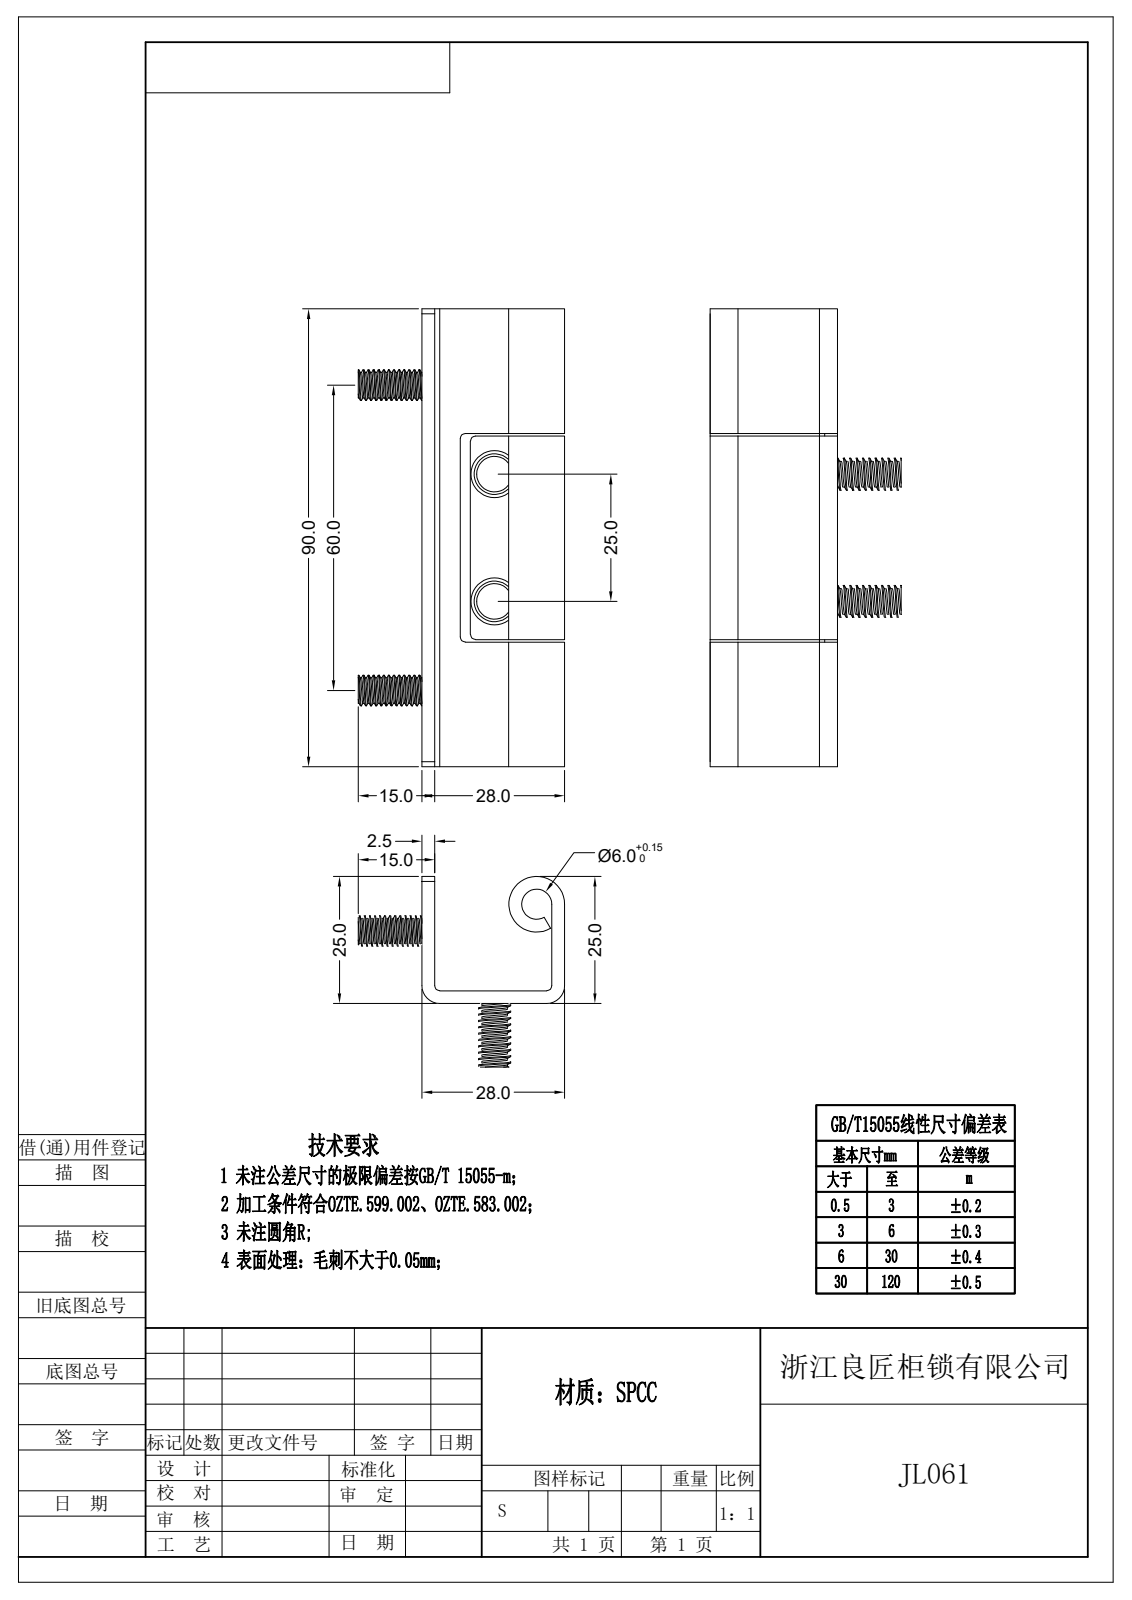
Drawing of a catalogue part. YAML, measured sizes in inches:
step_written_by: "Rhino 8.5 (CONFIG_CONTROL_DESIGN)"
units: inches
bodies: {solids: 6, faces: 188, planar: 40, cylindrical: 132, other: 16}
overall_size: [3.543, 1.594, 1.476]
volume: 1.262
surface_area: 29.02
round_holes:
  - {diameter: 0.248, count: 4}
  - {diameter: 0.236, count: 1}
round_bosses_or_shafts:
  - {diameter: 0.211, count: 4}
  - {diameter: 0.433, count: 1}
partial_cylinders:
  - {radius: 0.039, count: 8}
  - {radius: 0.138, count: 2}
face_to_face_distances: [0.098, 1.004, 1.102, 0.906, 0.984, 1.594, 0.965, 2.579, 2.559, 0.02]
hole_center_spacings: [0.984, 2.362]
